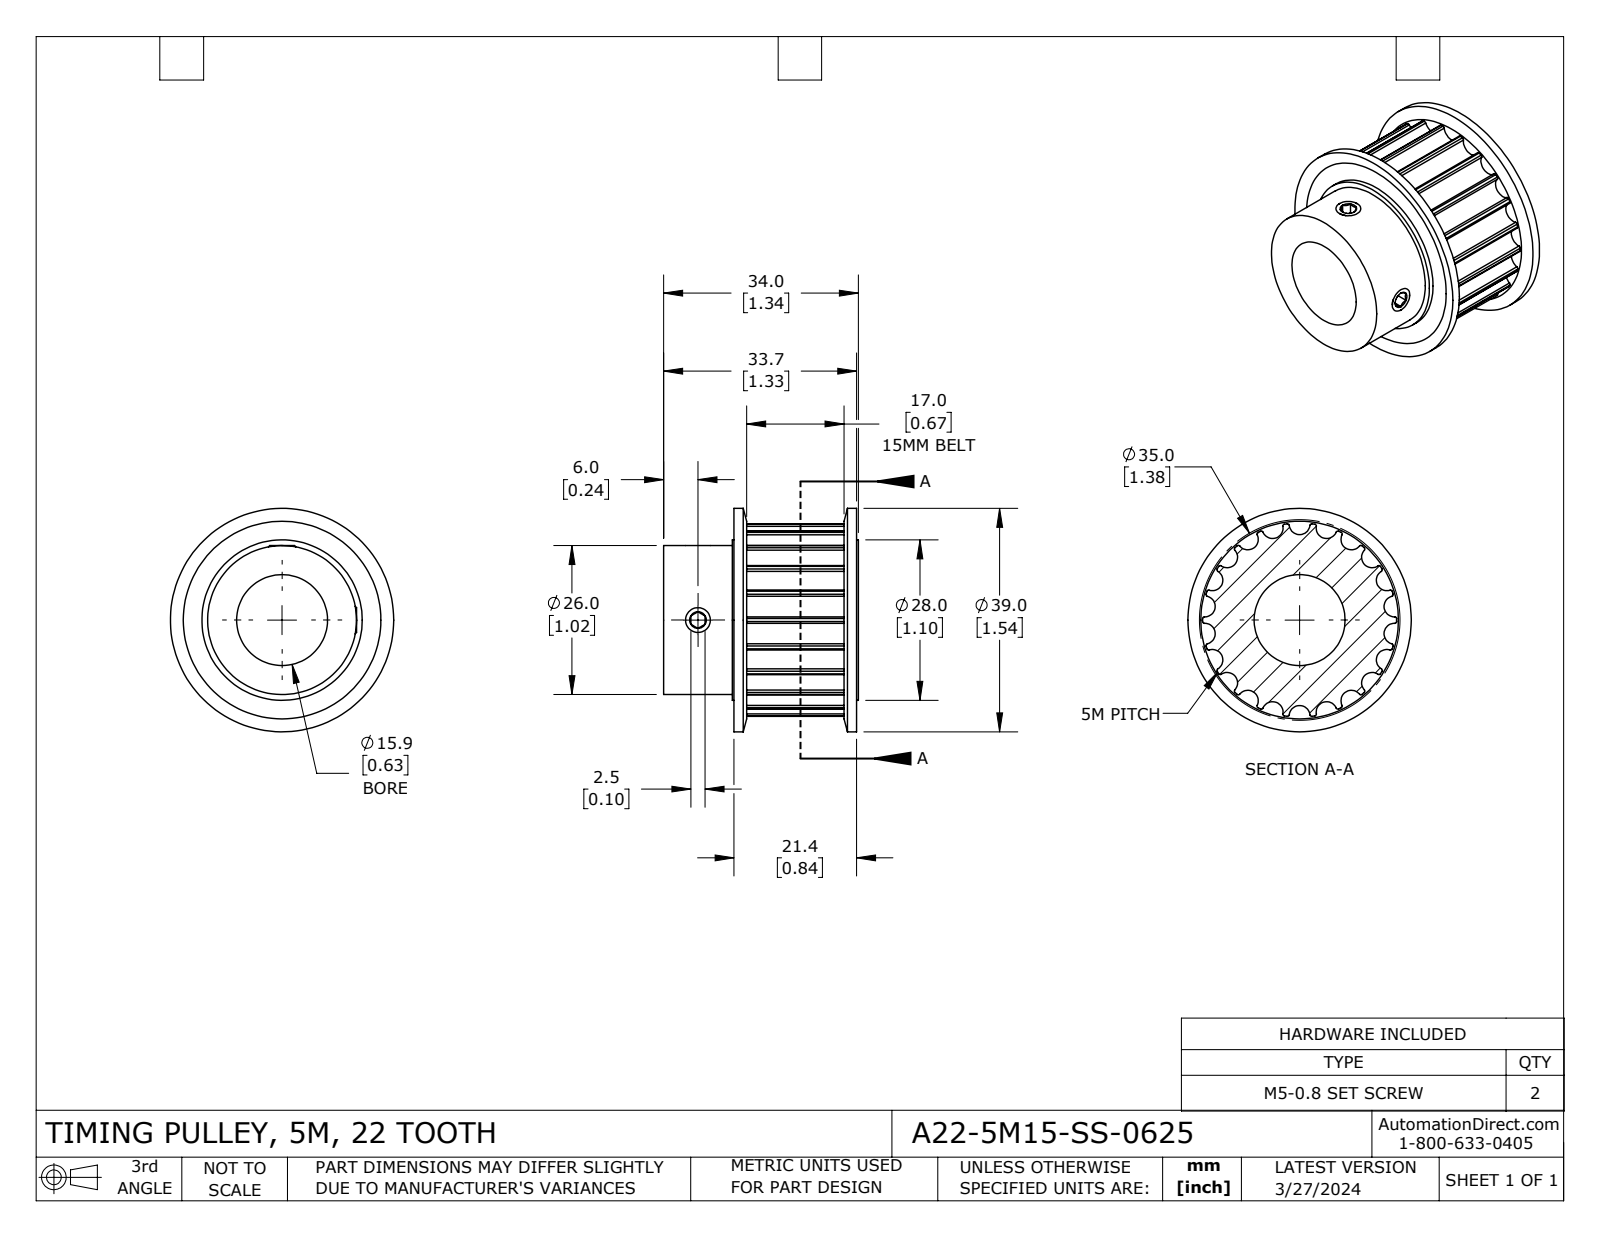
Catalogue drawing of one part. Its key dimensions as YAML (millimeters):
part_name: "A22-5M15-SS-0625"
step_written_by: "SolidWorks 2021 (CONFIG_CONTROL_DESIGN)"
units: millimeters
bodies: {solids: 5, faces: 192, planar: 25, cylindrical: 133, other: 34}
overall_size: [39, 39, 34]
volume: 17681
surface_area: 10130
round_holes:
  - {diameter: 4.2, count: 2}
  - {diameter: 15.88, count: 1}
  - {diameter: 28, count: 1}
round_bosses_or_shafts:
  - {diameter: 5, count: 2}
  - {diameter: 39, count: 1}
  - {diameter: 26, count: 1}
partial_cylinders:
  - {radius: 0.3, count: 44}
  - {radius: 1.82, count: 22}
  - {radius: 16.93, count: 1}
face_to_face_distances: [1.6, 18.6, 2.5, 19.5, 17, 0.9, 21.1, 34, 31.5, 14.5]
